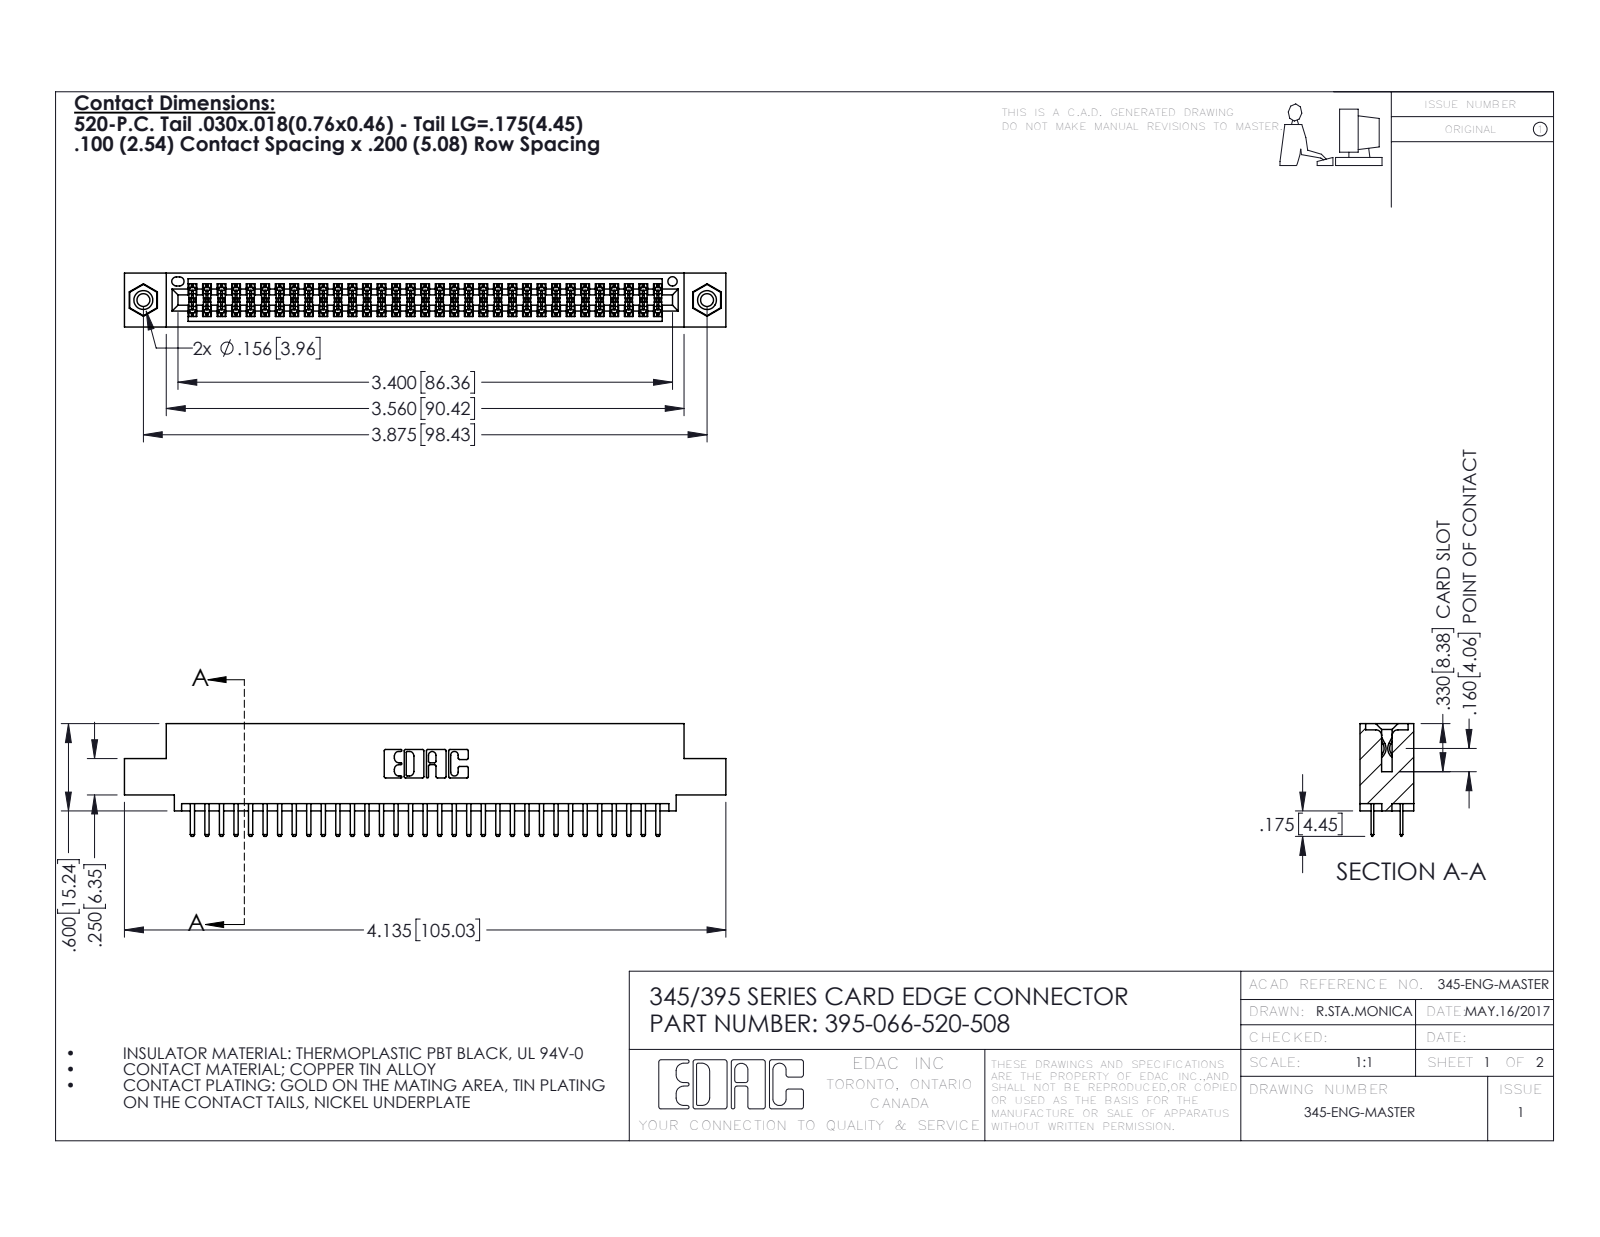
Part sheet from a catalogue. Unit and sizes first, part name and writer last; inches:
Units: inches
Overall size (bounding box): 4.135 × 0.775 × 0.37
Round holes (diameter × count): ⌀0.089 ×2, ⌀0.125 ×2, ⌀0.156 ×2, ⌀0.064 ×1
Round bosses / shafts (diameter × count): ⌀0.155 ×2
Partial cylindrical surfaces — rounded edges, fillets, slot ends (radius × count): R0.006 ×99, R0.01 ×70, R0.01 ×22, R0.007 ×6, R0.031 ×6, R0.026 ×3, R0.014 ×2, R0.019 ×2
Main face-to-face distances: 0.072, 0.298, 0.2, 0.37, 0.098, 0.272, 0.025, 0.225, 0.022, 0.072
Hole centre spacings: 0.27, 3.64, 3.875
Volume: 0.611 in³ · Surface area: 22.73 in²
Bodies: 69 solids, 3754 faces (2426 planar, 1312 cylindrical, 16 other)
Part name (STEP PRODUCT): 395-066-520-508; 345-292-001_345-293-120; 345-250-001_345-250-003-102; 345 Part_0.110 Offset - 0.156 Dia-TI
STEP written by: SolidWorks 2016 (CONFIG_CONTROL_DESIGN)
